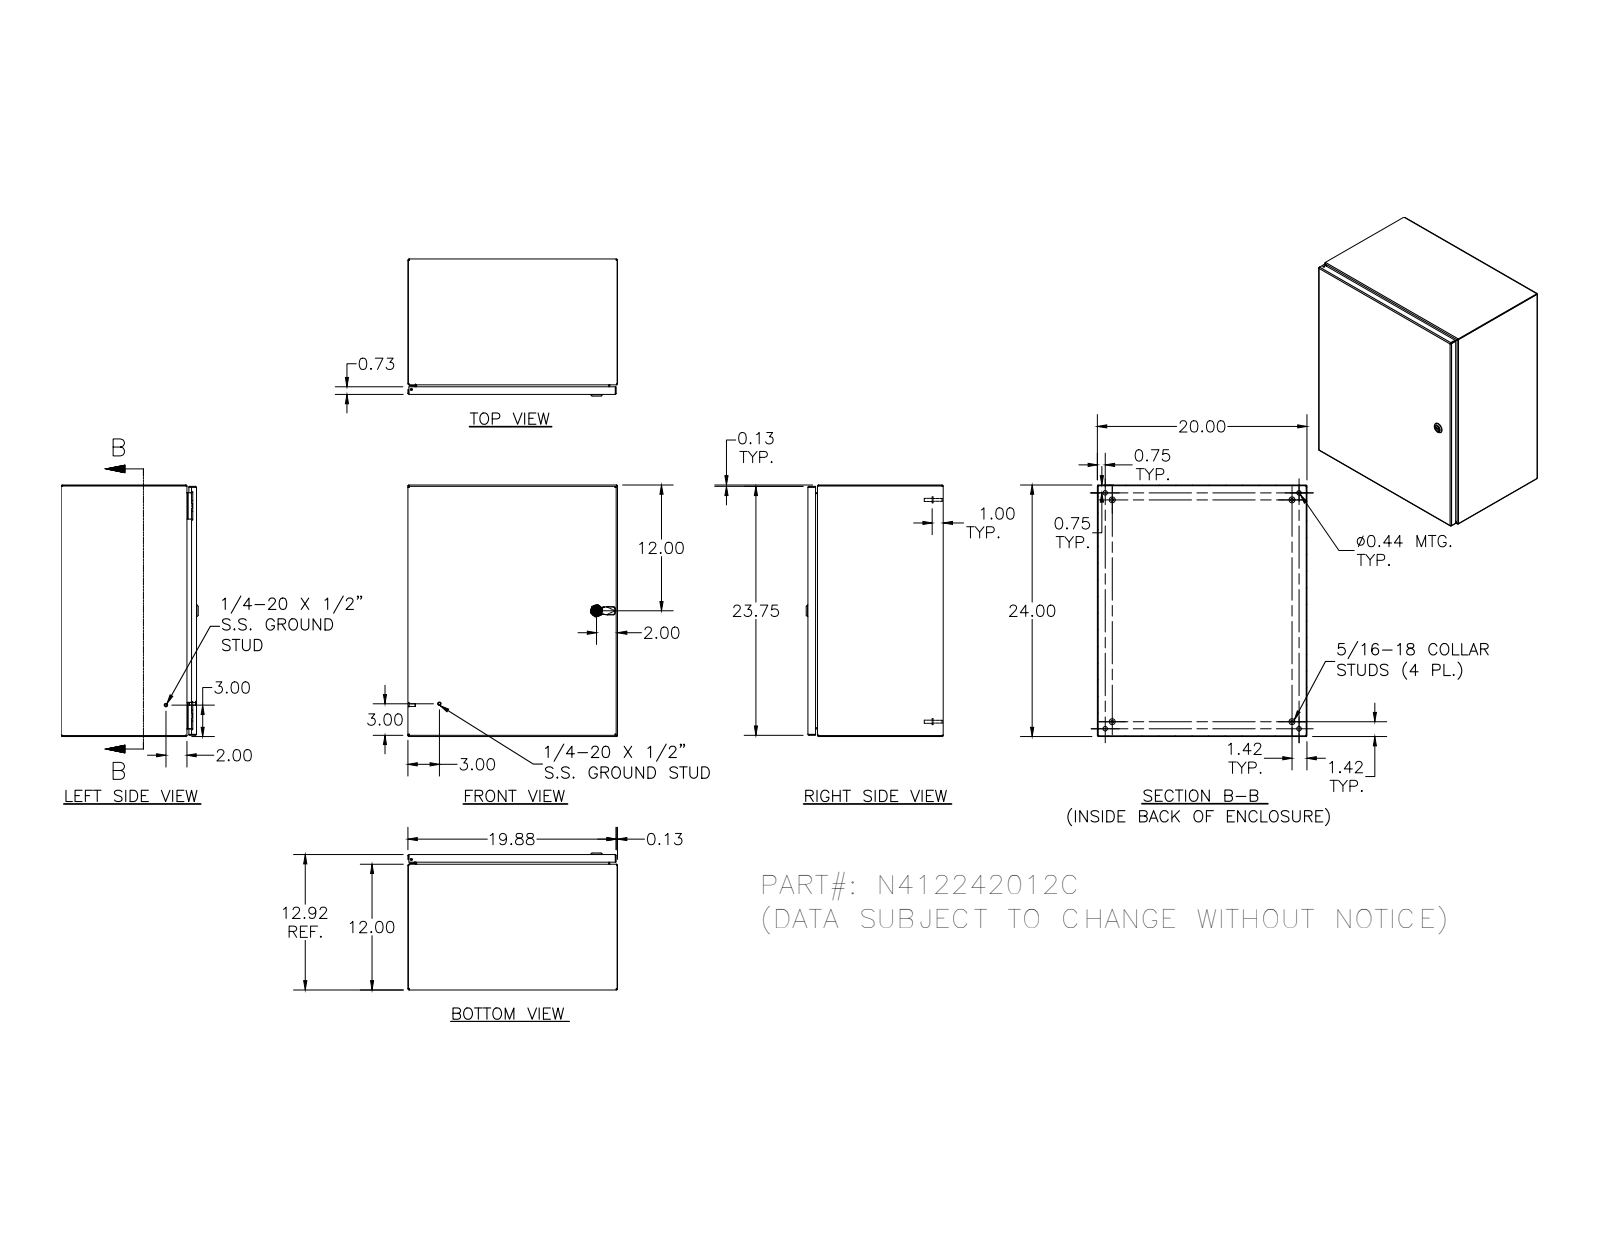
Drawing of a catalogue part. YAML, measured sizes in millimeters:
part_name: "N412242012C"
step_written_by: "SolidWorks 2018 (AUTOMOTIVE_DESIGN)"
units: millimeters
bodies: {solids: 33, faces: 1449, planar: 530, cylindrical: 547, other: 372}
overall_size: [609.6, 508, 332.1]
volume: 2656000
surface_area: 2841000
round_holes:
  - {diameter: 4.8, count: 5}
  - {diameter: 2.4, count: 4}
  - {diameter: 3.9, count: 4}
  - {diameter: 4.2, count: 4}
  - {diameter: 4.4, count: 4}
  - {diameter: 11.1, count: 4}
  - {diameter: 4, count: 2}
  - {diameter: 4.7, count: 1}
  - {diameter: 5, count: 1}
  - {diameter: 8, count: 1}
  - {diameter: 10, count: 1}
  - {diameter: 10.2, count: 1}
round_bosses_or_shafts:
  - {diameter: 6.4, count: 10}
  - {diameter: 14.3, count: 4}
  - {diameter: 9.1, count: 4}
  - {diameter: 8.1, count: 4}
  - {diameter: 7.6, count: 4}
  - {diameter: 6.5, count: 4}
  - {diameter: 4.2, count: 4}
  - {diameter: 3.3, count: 4}
partial_cylinders:
  - {radius: 0.3, count: 30}
  - {radius: 0.8, count: 30}
  - {radius: 1.3, count: 26}
  - {radius: 2.7, count: 20}
  - {radius: 0.4, count: 18}
  - {radius: 3.2, count: 16}
  - {radius: 0.5, count: 13}
  - {radius: 0.8, count: 8}
face_to_face_distances: [1.9, 326.2, 1.9, 324.3, 328.1, 506.1, 508, 504.2, 506.1, 607.7]
hole_center_spacings: [508, 16.8, 16.7, 33.2, 49.9, 479.3, 12.7, 25]
